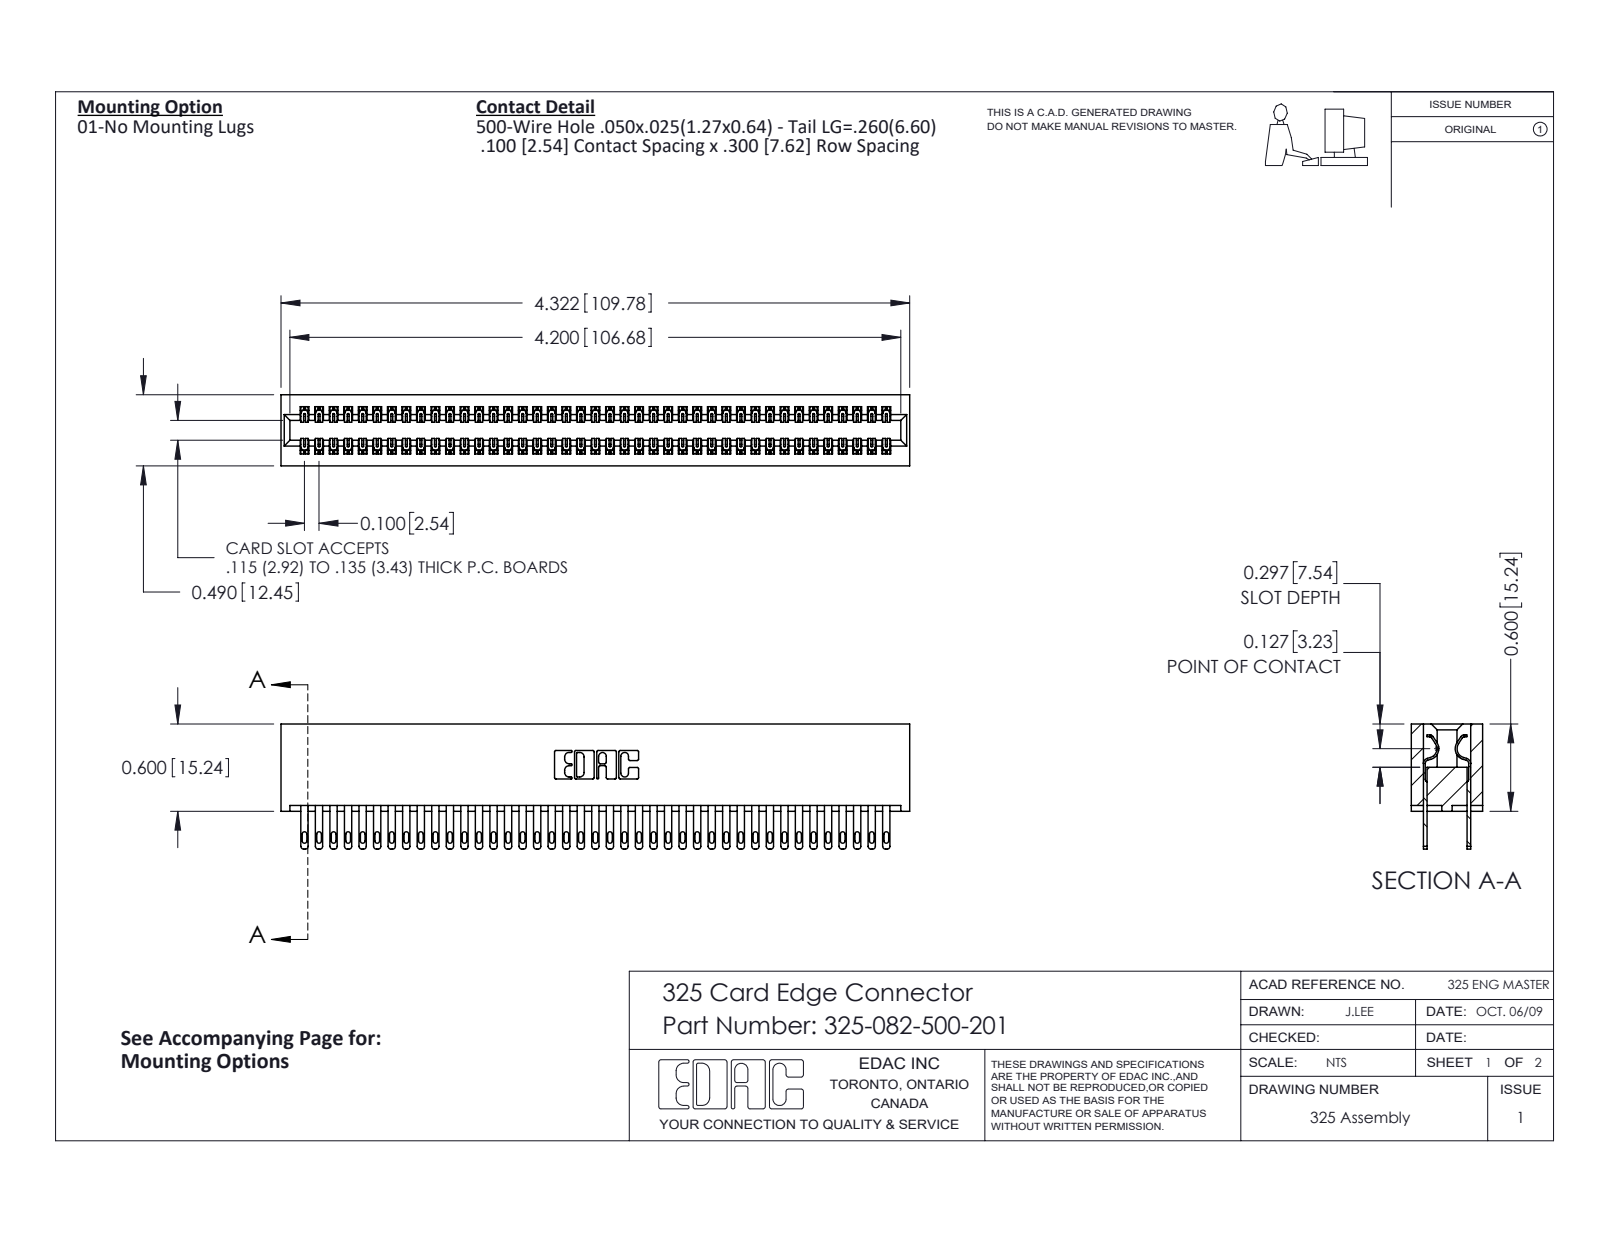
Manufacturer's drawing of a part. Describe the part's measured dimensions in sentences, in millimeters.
The part is named "325 Part_Lugless; 325-082-500-201; 325-292-001_325-293-100". Its 3-D file was written by "SolidWorks 2016 (CONFIG_CONTROL_DESIGN)". It is 83 solids with 4042 faces: 2526 planar, 1516 cylindrical and 0 other. Overall it measures 109.8 by 21.8 by 12.4 millimeters. Its volume is 15 000 cubic millimeters and its surface area 19 670 square millimeters. Partial cylindrical surfaces (rounded edges, fillets, slot ends): 123 of radius 0.2, 82 of radius 0.4, 82 of radius 0.5, 22 of radius 0.3, 6 of radius 0.2, 6 of radius 0.8, 3 of radius 0.7, 2 of radius 0.4. The main face-to-face distances are 2.1, 10.3, 7.6, 2.7, 9.7, 0.6, 8.3, 12.4, 7, 14.2.
